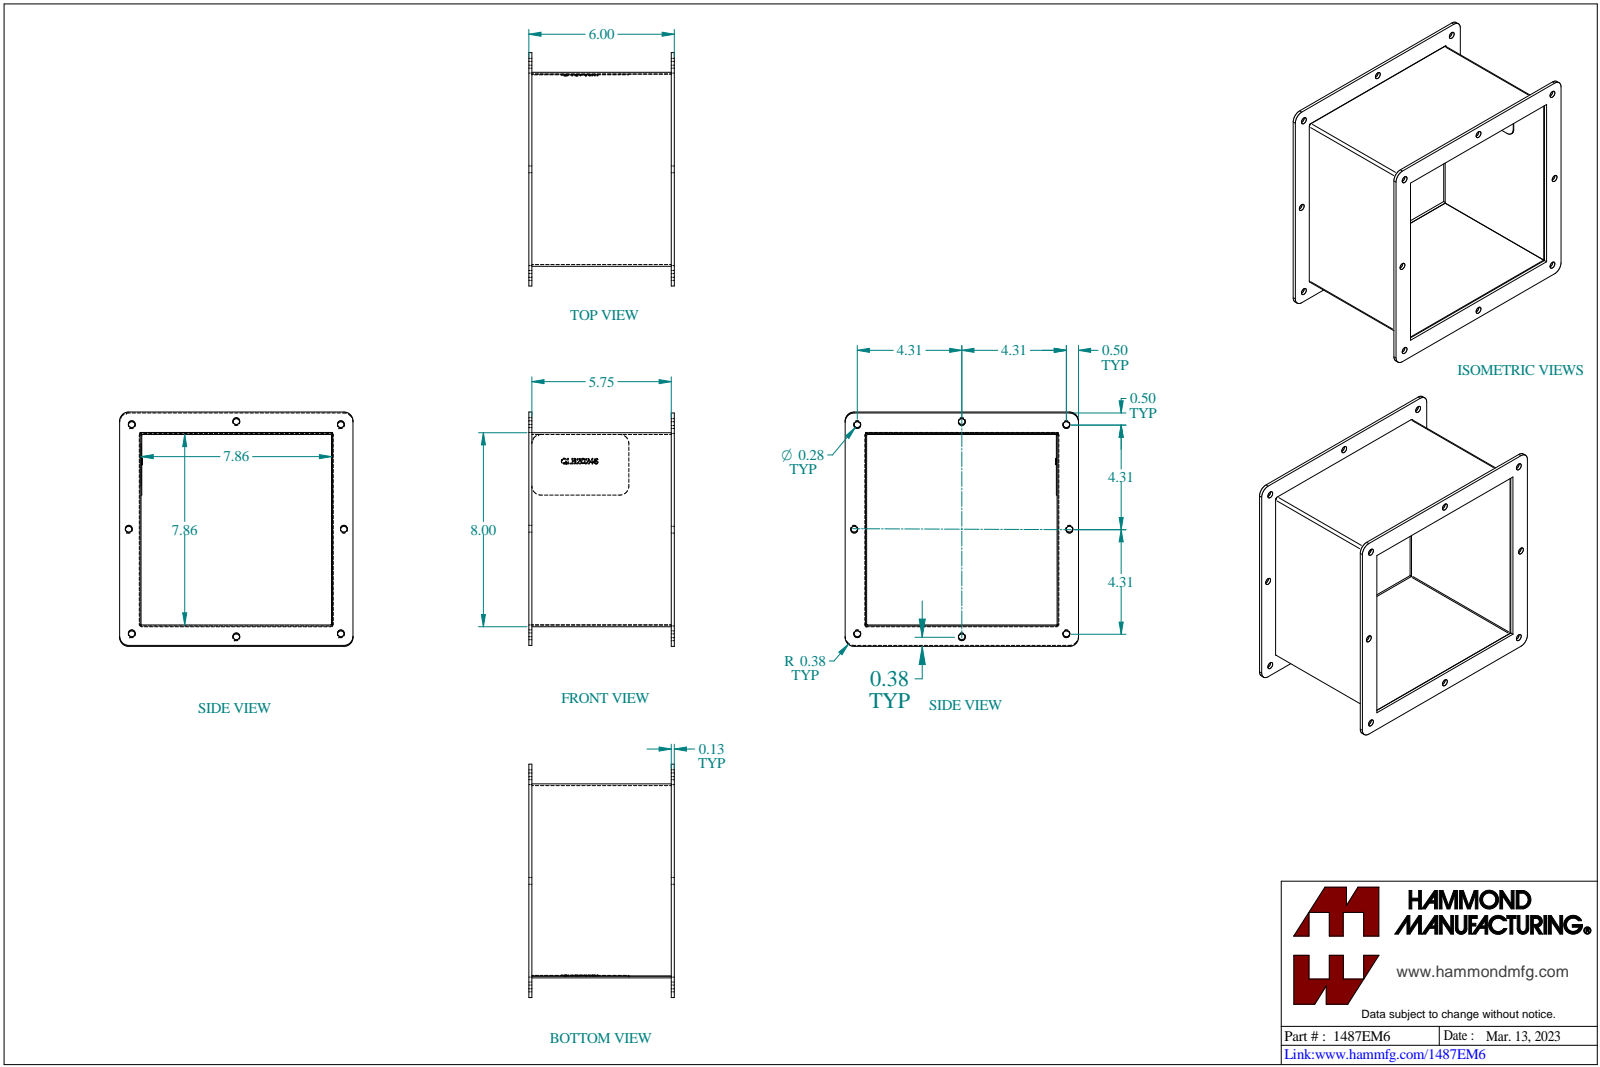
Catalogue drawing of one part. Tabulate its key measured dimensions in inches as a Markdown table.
| quantity | value |
| --- | --- |
| part name | 1487EM6 |
| STEP written by | SolidWorks 2023 (CONFIG_CONTROL_DESIGN) |
| units | inches |
| bodies | 4 solids, 112 faces (42 planar, 70 cylindrical, 0 other) |
| overall size | 9.665 × 9.625 × 6.125 |
| volume | 23.94 in³ |
| surface area | 570.9 in² |
| round holes (diameter × count) | 0.281 × 16 |
| partial cylindrical surfaces (radius × count) | 0.375 × 8, 0.25 × 4, 0.036 × 3, 0.108 × 3 |
| main face-to-face distances | 0.072, 7.928, 8, 7.856, 0.125, 5.875, 6, 5.75, 0.25, 6.125 |
| hole center spacings | 4.315, 9.755, 8.625, 6.276, 0.04, 8.875, 4.313, 4.316 |
